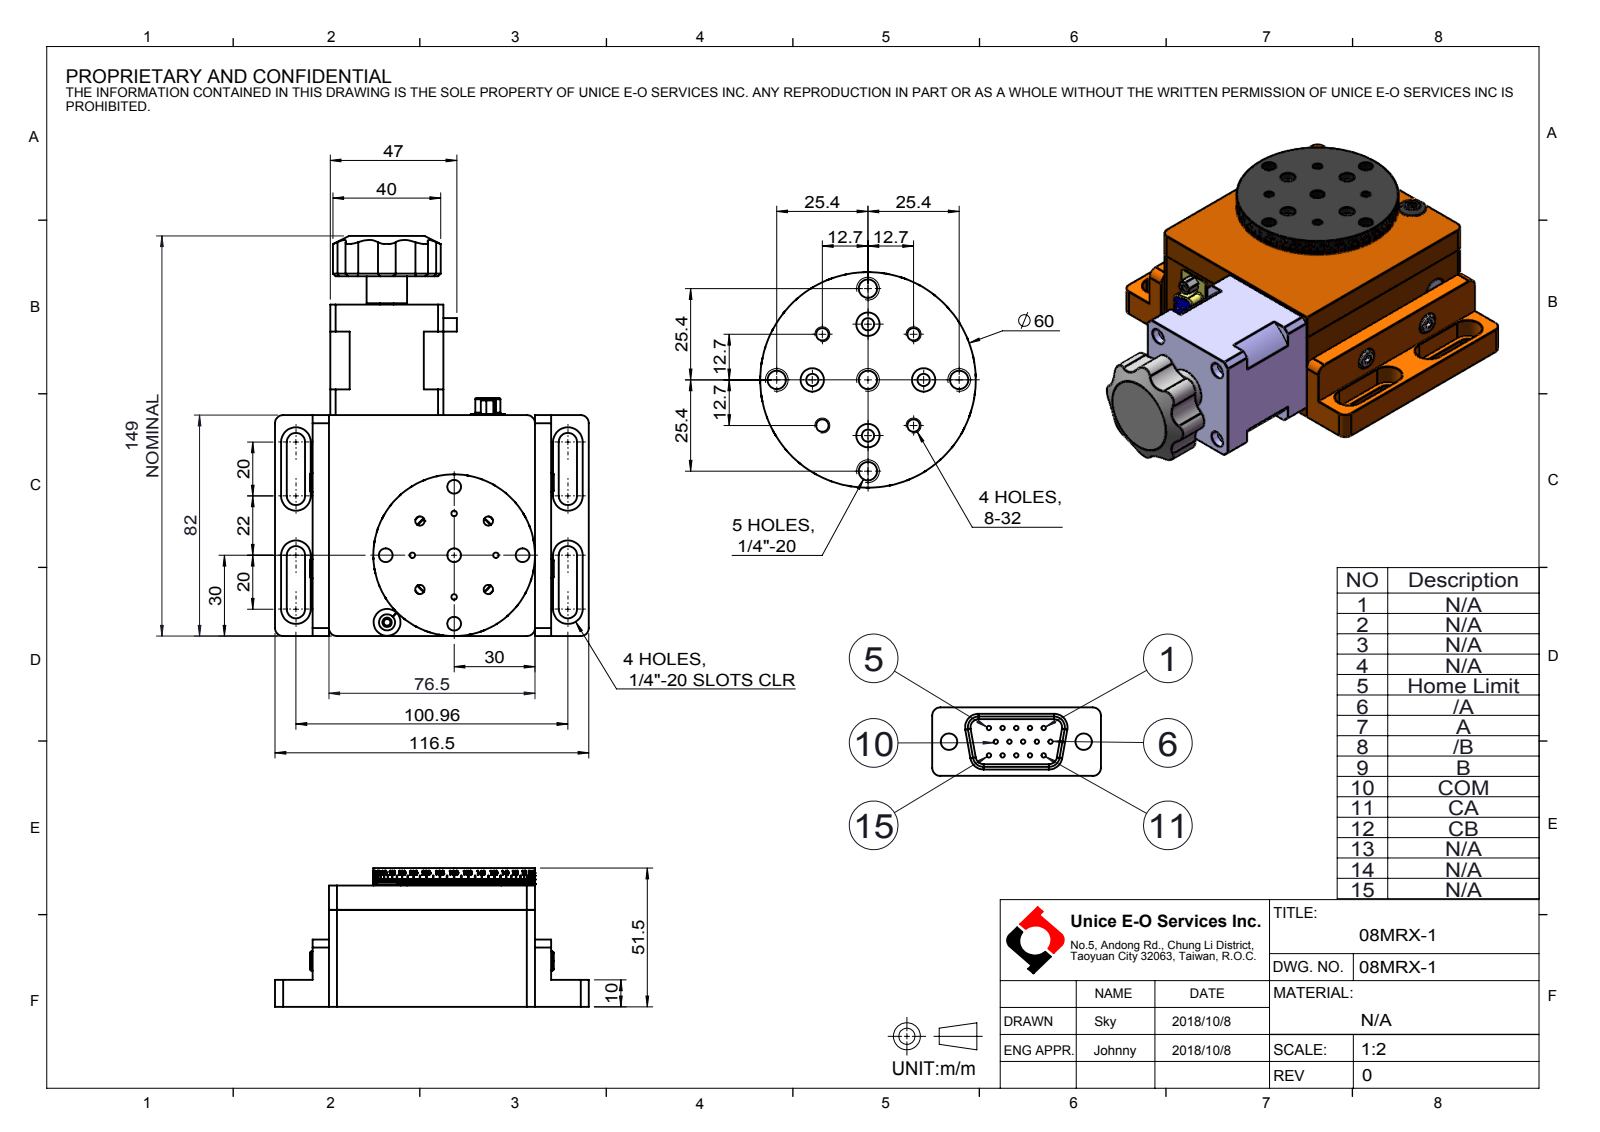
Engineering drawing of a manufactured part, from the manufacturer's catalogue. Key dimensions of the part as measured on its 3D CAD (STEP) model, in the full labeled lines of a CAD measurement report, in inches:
Part name (STEP PRODUCT): 08MRX-1
STEP written by: SolidWorks 2016 (AUTOMOTIVE_DESIGN)
Units: inches
Bodies: 0 solids, 915 faces (372 planar, 352 cylindrical, 191 other)
Overall size (bounding box): 5.846 × 4.587 × 2.028
Round holes (diameter × count): ⌀0.031 ×15, ⌀0.201 ×5, ⌀0.087 ×4, ⌀0.098 ×4, ⌀0.114 ×4, ⌀0.136 ×4, ⌀0.217 ×4, ⌀0.236 ×4, ⌀0.24 ×4, ⌀0.13 ×2, ⌀0.315 ×2, ⌀0.039 ×1
Round bosses / shafts (diameter × count): ⌀0.276 ×2, ⌀2.362 ×1, ⌀1.693 ×1, ⌀0.591 ×1, ⌀0.394 ×1
Partial cylindrical surfaces — rounded edges, fillets, slot ends (radius × count): R0.118 ×9, R0.02 ×8, R0.134 ×8, R0.157 ×8, R0.217 ×8, R0.292 ×8, R0.059 ×4, R0.079 ×4
Main face-to-face distances: 0.354, 3.012, 1.772, 0.039, 1.417, 3.228, 0.256, 0.236, 1.654, 1.339
Hole centre spacings: 0.112, 0.18, 0.2, 0.1, 0.707, 0.269, 1, 0.224
